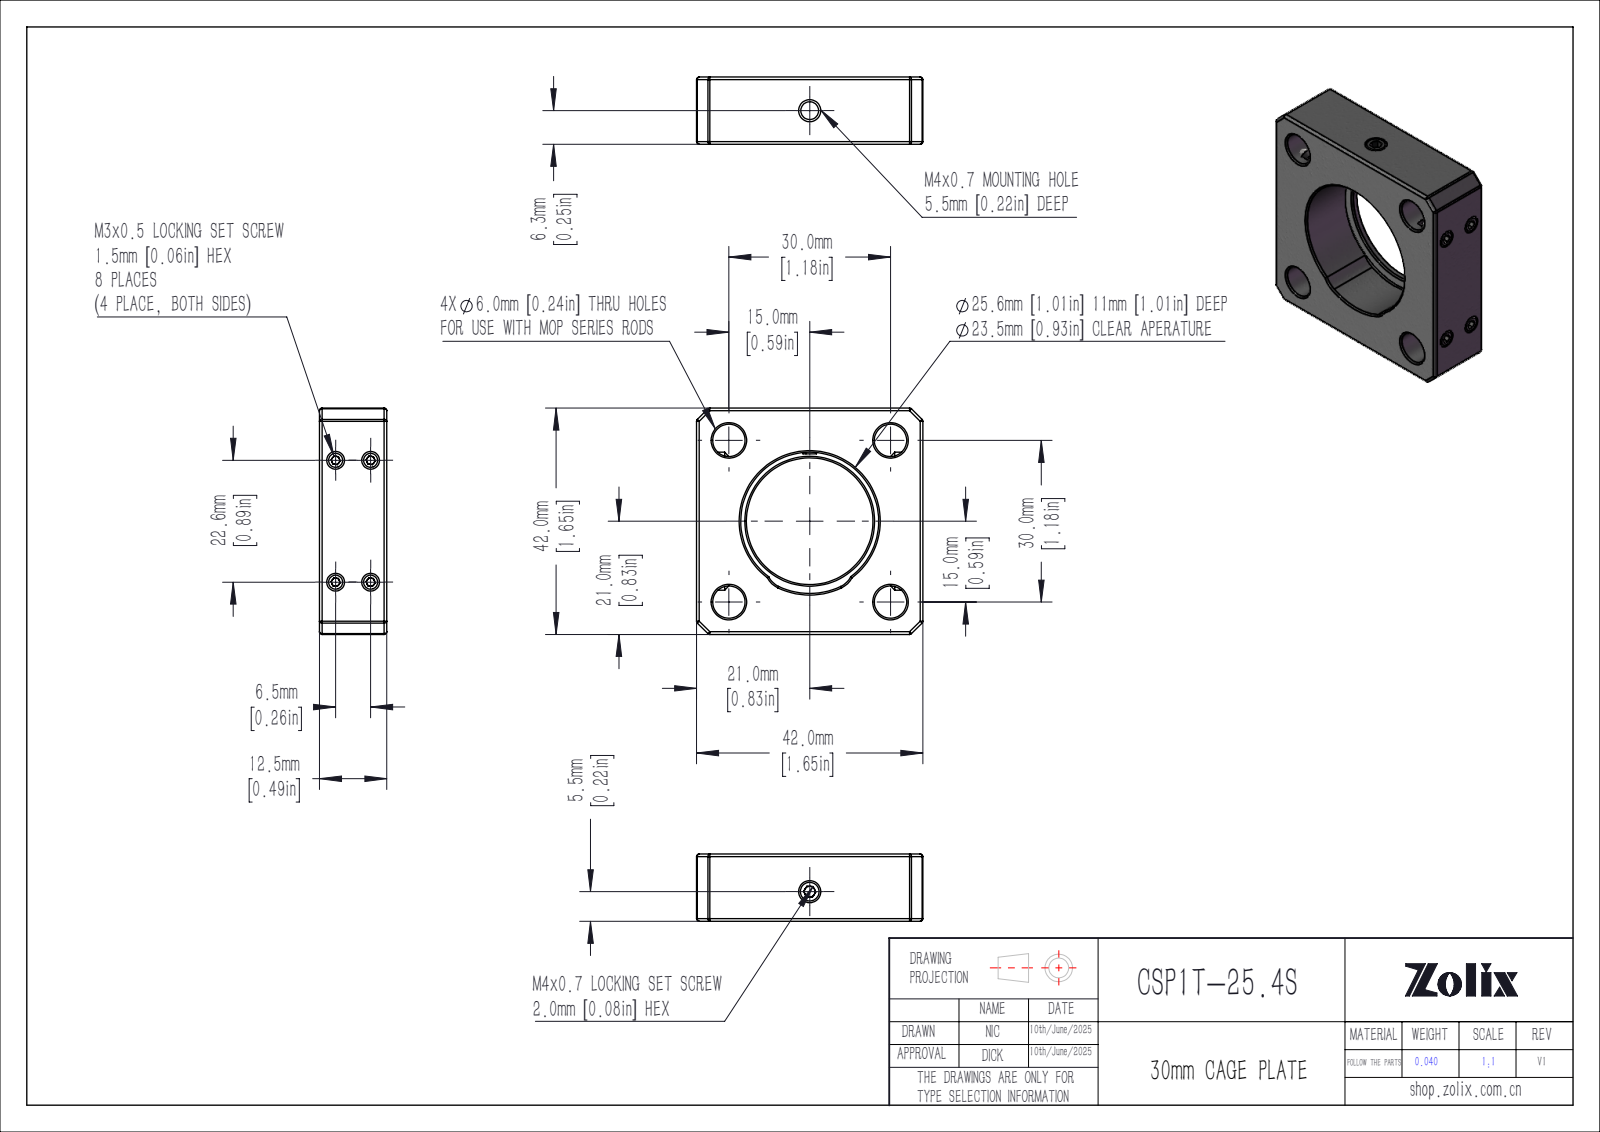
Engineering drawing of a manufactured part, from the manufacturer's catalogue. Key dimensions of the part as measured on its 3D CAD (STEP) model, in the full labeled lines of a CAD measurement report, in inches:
Part name (STEP PRODUCT): CSP1T-25.4S
STEP written by: SolidWorks 2020 (CONFIG_CONTROL_DESIGN)
Units: inches
Bodies: 10 solids, 682 faces (357 planar, 82 cylindrical, 243 other)
Overall size (bounding box): 1.654 × 1.654 × 0.492
Volume: 0.855 in³ · Surface area: 11.68 in²
Round holes (diameter × count): ⌀0.098 ×4, ⌀0.236 ×4, ⌀0.13 ×2, ⌀0.925 ×1, ⌀1.008 ×1, ⌀1.075 ×1
Round bosses / shafts (diameter × count): ⌀0.118 ×4, ⌀0.157 ×1, ⌀0.098 ×1
Partial cylindrical surfaces — rounded edges, fillets, slot ends (radius × count): R0.02 ×24, R0.157 ×2, R0.528 ×1
Main face-to-face distances: 0.492, 1.654, 0.059, 0.433, 2.213, 0.091, 0.031, 0.402, 0.491, 0.432
Hole centre spacings: 0.835, 1.181, 0.256, 0.89, 0.926, 1.67, 0.03
